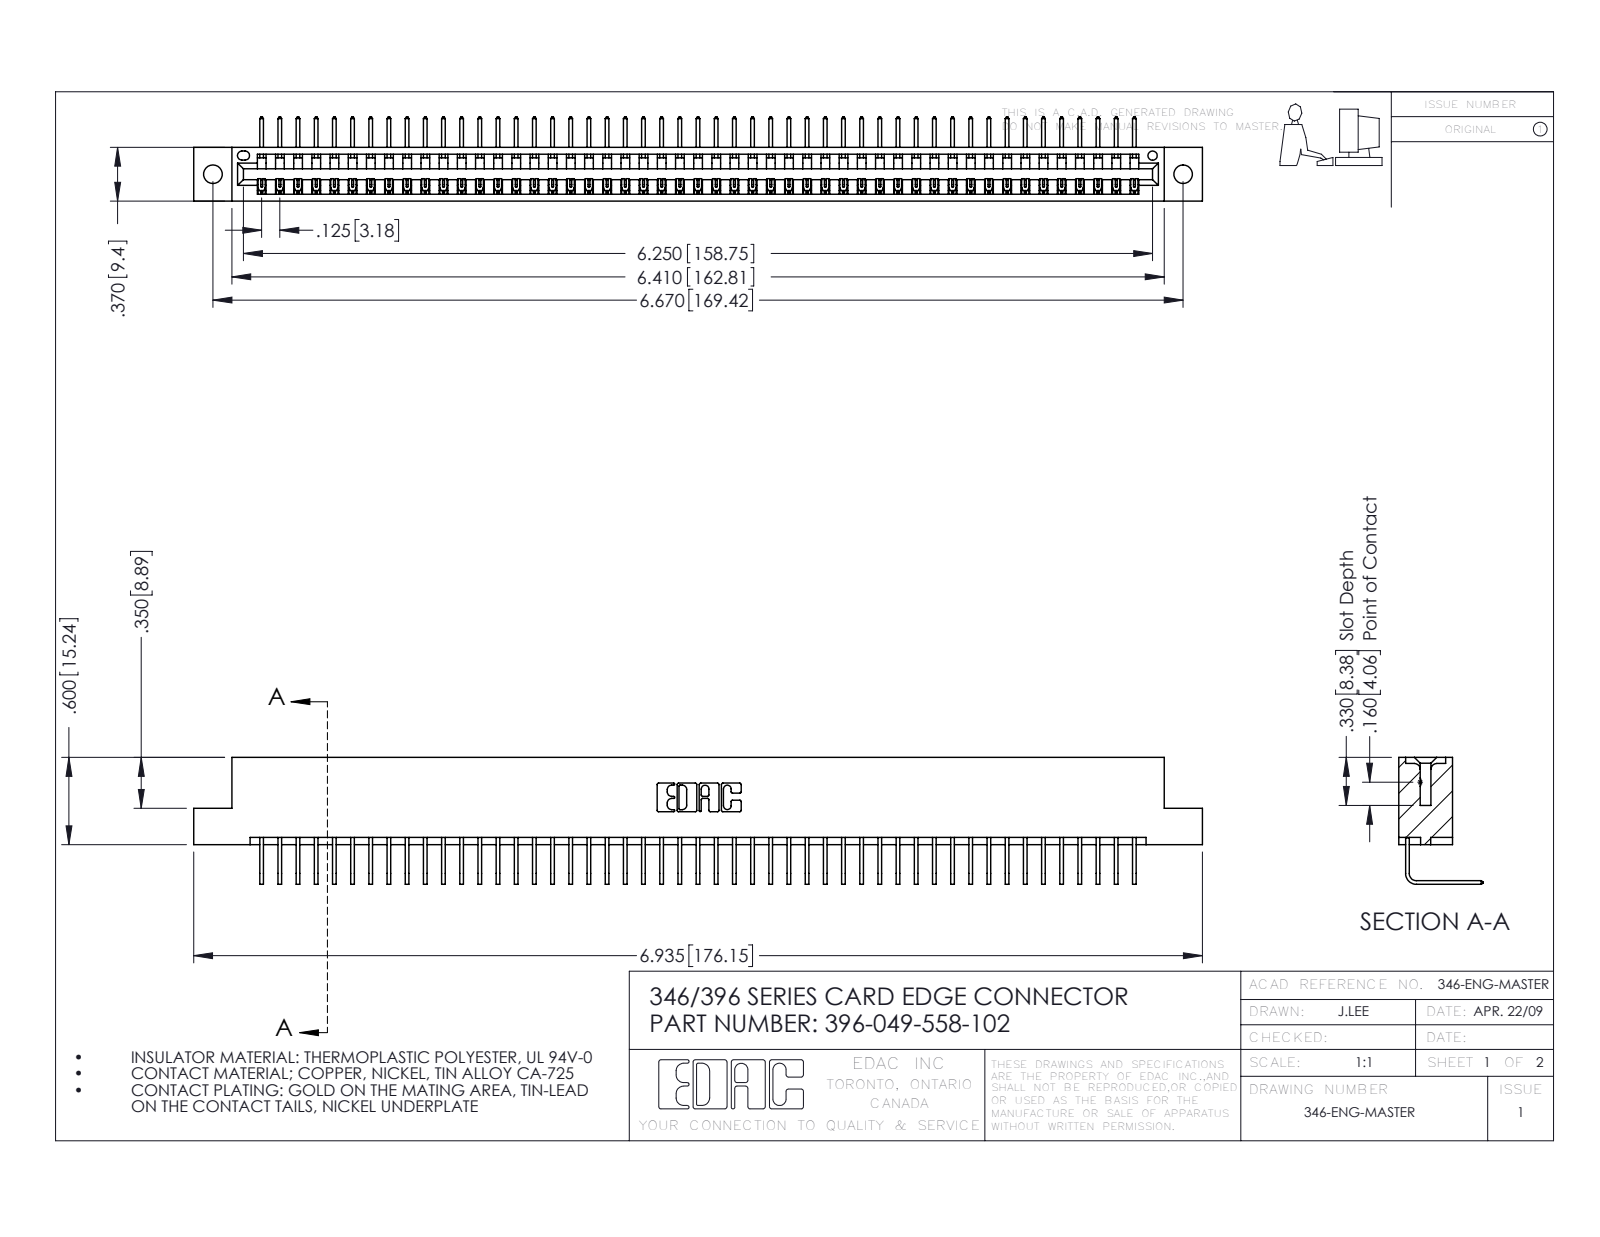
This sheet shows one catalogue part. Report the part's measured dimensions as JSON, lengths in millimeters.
{"part_name": "396-049-558-102; 345-292-001_558 Tail - 2; 346 Part_Flush Mounting Lugs - 0.128 Dia", "step_written_by": "SolidWorks 2016 (CONFIG_CONTROL_DESIGN)", "units": "millimeters", "bodies": {"solids": 50, "faces": 3062, "planar": 2134, "cylindrical": 928, "other": 0}, "overall_size": [176.1, 22.2, 14.7], "volume_mm3": 17040, "surface_area_mm2": 22070, "round_holes": [[3.3, 2], [1.6, 1]], "partial_cylinders_radius": [[0.2, 98], [0.3, 22], [0.2, 6], [0.8, 6], [0.7, 3], [0.8, 2], [1, 2], [0.4, 1]], "face_to_face_distances": [8.2, 1.2, 9.4, 6.4, 7.6, 0.6, 1.8, 3.8, 5.6, 2.5], "hole_center_spacings": [6.2, 164.1, 169.4]}
